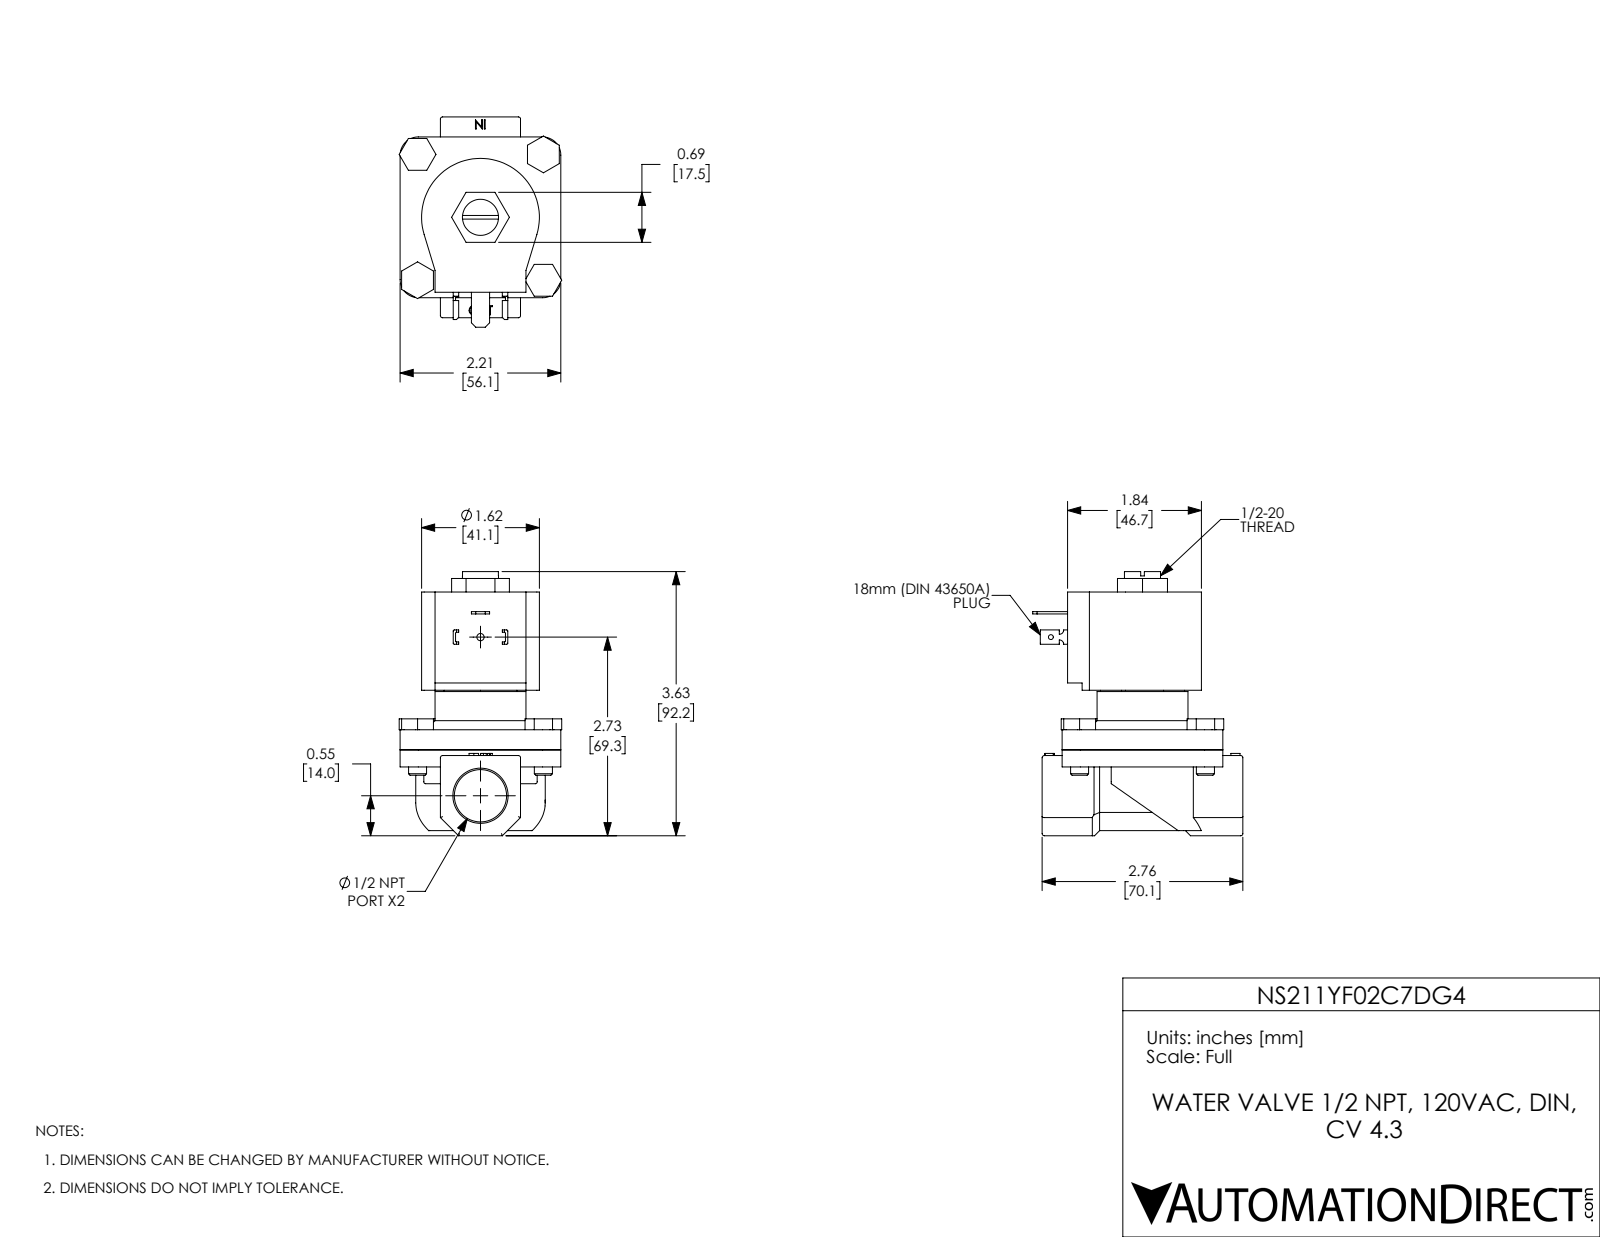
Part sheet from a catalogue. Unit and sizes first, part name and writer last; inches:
Units: inches
Overall size (bounding box): 3.63 × 2.89 × 2.235
Round holes (diameter × count): ⌀0.25 ×4, ⌀0.067 ×1, ⌀0.1 ×1, ⌀0.496 ×1, ⌀0.512 ×1, ⌀0.719 ×1, ⌀1.155 ×1
Round bosses / shafts (diameter × count): ⌀0.248 ×4, ⌀1.25 ×1
Partial cylindrical surfaces — rounded edges, fillets, slot ends (radius × count): R0.03 ×15, R0.015 ×8, R0.25 ×4, R0.06 ×2, R0.81 ×1, R0.89 ×1
Main face-to-face distances: 0.276, 2.169, 1.893, 0.554, 1.656, 0.236, 0.512, 2.405, 2.21, 1.102
Hole centre spacings: 1.223, 1.73, 2.446, 2.18
Volume: 9.198 in³ · Surface area: 60.98 in²
Bodies: 11 solids, 330 faces (196 planar, 99 cylindrical, 35 other)
Part name (STEP PRODUCT): NS211YF02C7DG4
STEP written by: SolidWorks 2021 (CONFIG_CONTROL_DESIGN)
